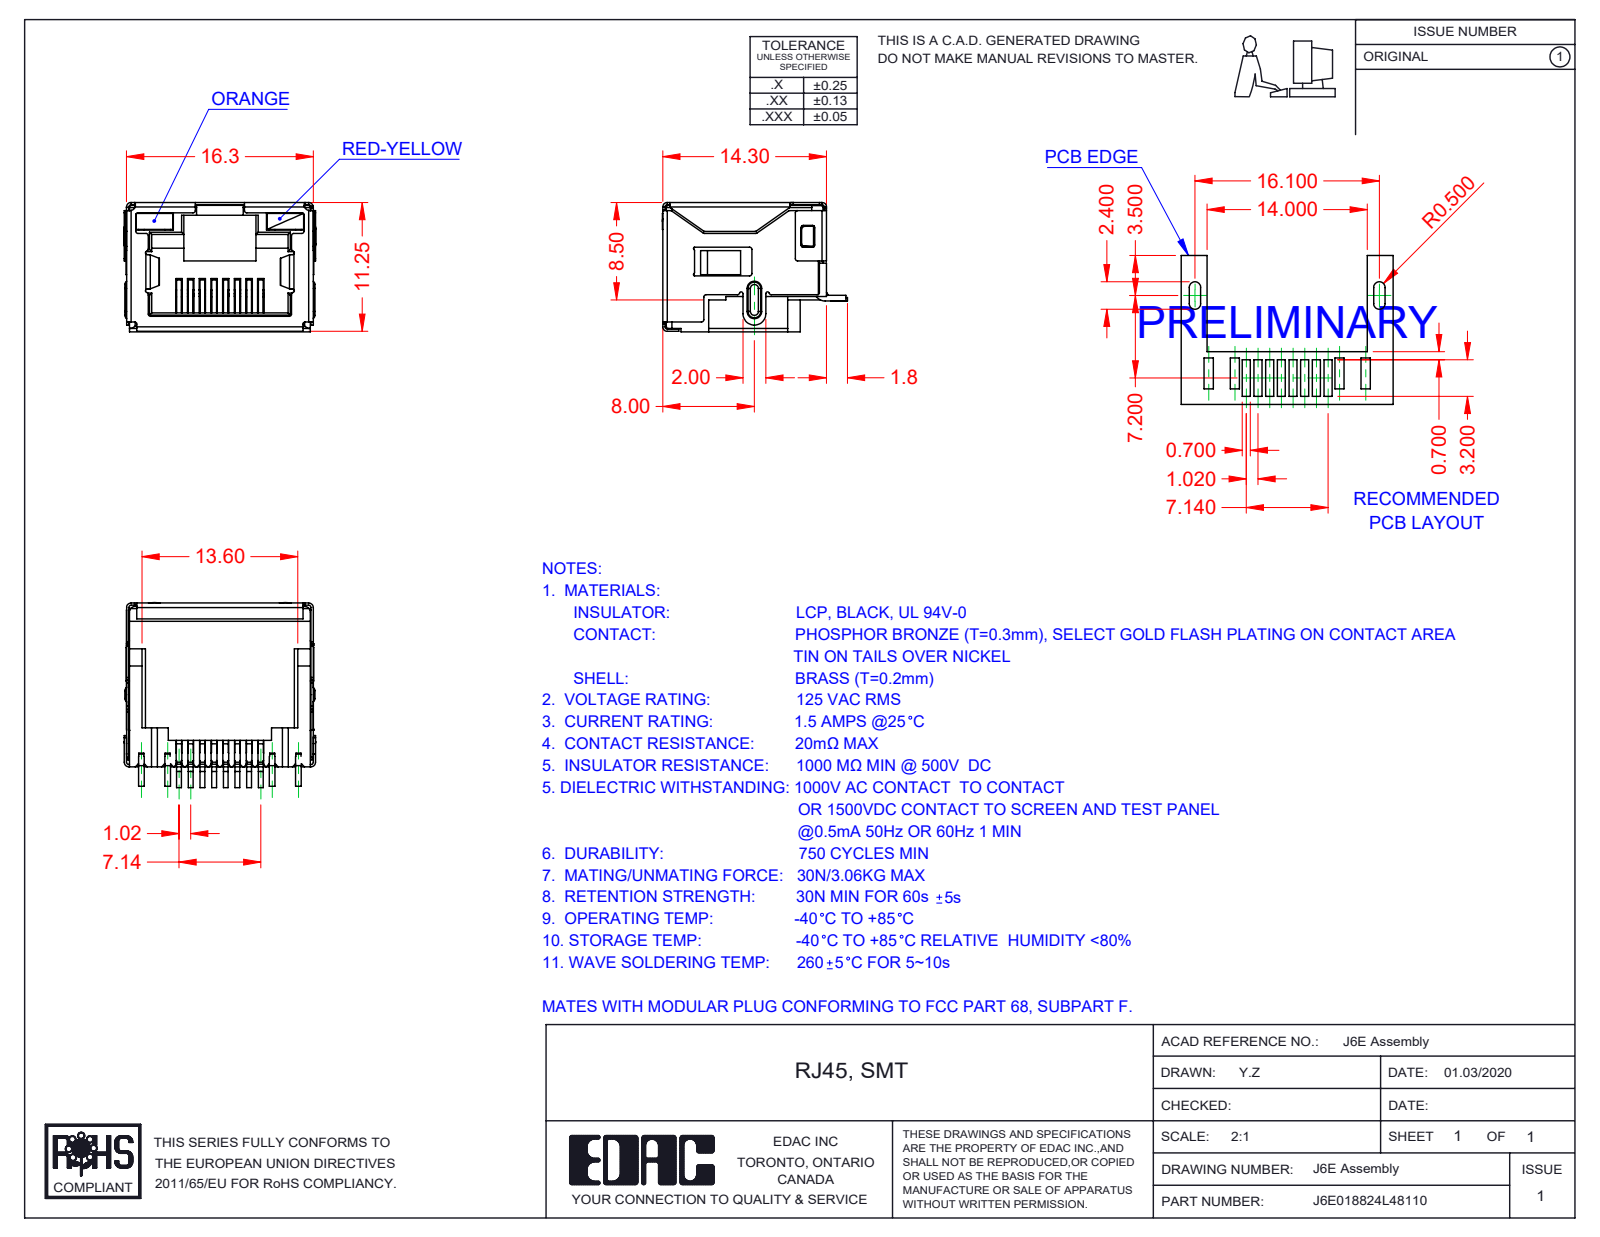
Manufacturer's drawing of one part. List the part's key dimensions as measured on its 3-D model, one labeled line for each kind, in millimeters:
Part name (STEP PRODUCT): J6E018824L48110; 6E LED LH_4-Orange; 6E Contacts; 6E Shield_LED (+2 more)
STEP written by: SolidWorks 2016 (CONFIG_CONTROL_DESIGN)
Units: millimetres
Bodies: 12 solids, 1498 faces (1099 planar, 349 cylindrical, 50 other)
Overall size (bounding box): 16.75 × 16.15 × 11.3
Volume: 1 109 mm³ · Surface area: 4 045 mm²
Partial cylindrical surfaces — rounded edges, fillets, slot ends (radius × count): R0.2 ×82, R0.25 ×17, R0.4 ×13, R0.5 ×13, R0.1 ×10, R0.15 ×7, R0.3 ×4, R1 ×3
Main face-to-face distances: 11.05, 16.05, 16.1, 15.85, 11.1, 11.3, 2.4, 0.7, 9.85, 0.49
